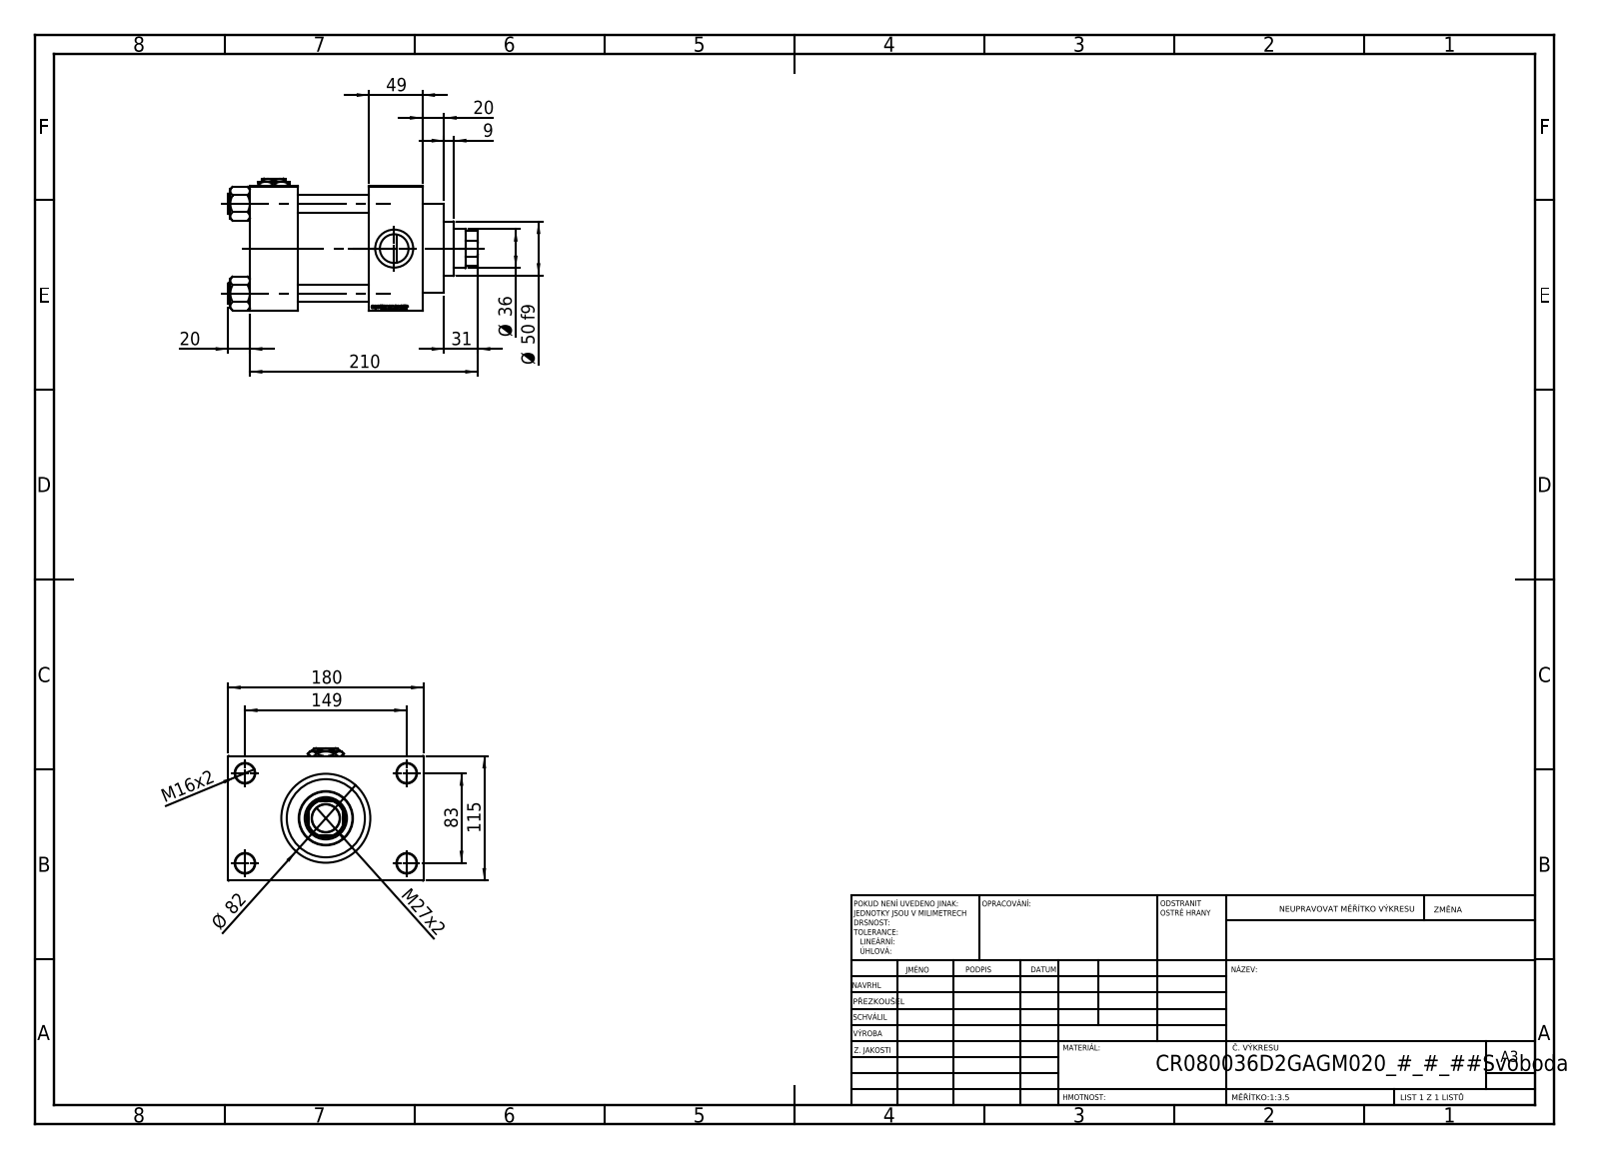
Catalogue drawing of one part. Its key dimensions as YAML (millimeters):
part_name: "V215CR_D_Body; Zatka_pro_OIL_PORT; NUT_M5_D; V215CR_VCP_D (+2 more)"
step_written_by: "SolidWorks 2019 (CONFIG_CONTROL_DESIGN)"
units: millimeters
bodies: {solids: 12, faces: 1194, planar: 567, cylindrical: 89, other: 538}
overall_size: [230, 180, 122]
volume: 1983000
surface_area: 298618
round_holes:
  - {diameter: 16, count: 4}
  - {diameter: 18, count: 4}
  - {diameter: 7, count: 2}
  - {diameter: 26.44, count: 2}
  - {diameter: 35, count: 2}
  - {diameter: 25.5, count: 1}
  - {diameter: 36, count: 1}
  - {diameter: 39, count: 1}
  - {diameter: 61, count: 1}
  - {diameter: 72, count: 1}
  - {diameter: 80, count: 1}
round_bosses_or_shafts:
  - {diameter: 19, count: 4}
  - {diameter: 86, count: 1}
  - {diameter: 82, count: 1}
  - {diameter: 50, count: 1}
partial_cylinders:
  - {radius: 17.5, count: 1}
face_to_face_distances: [115, 66, 110, 49, 44, 159, 32.5, 147.5, 20, 69]
hole_center_spacings: [33.15, 58.48, 82.7, 85.28, 89.24, 115.85, 142.43, 83]
